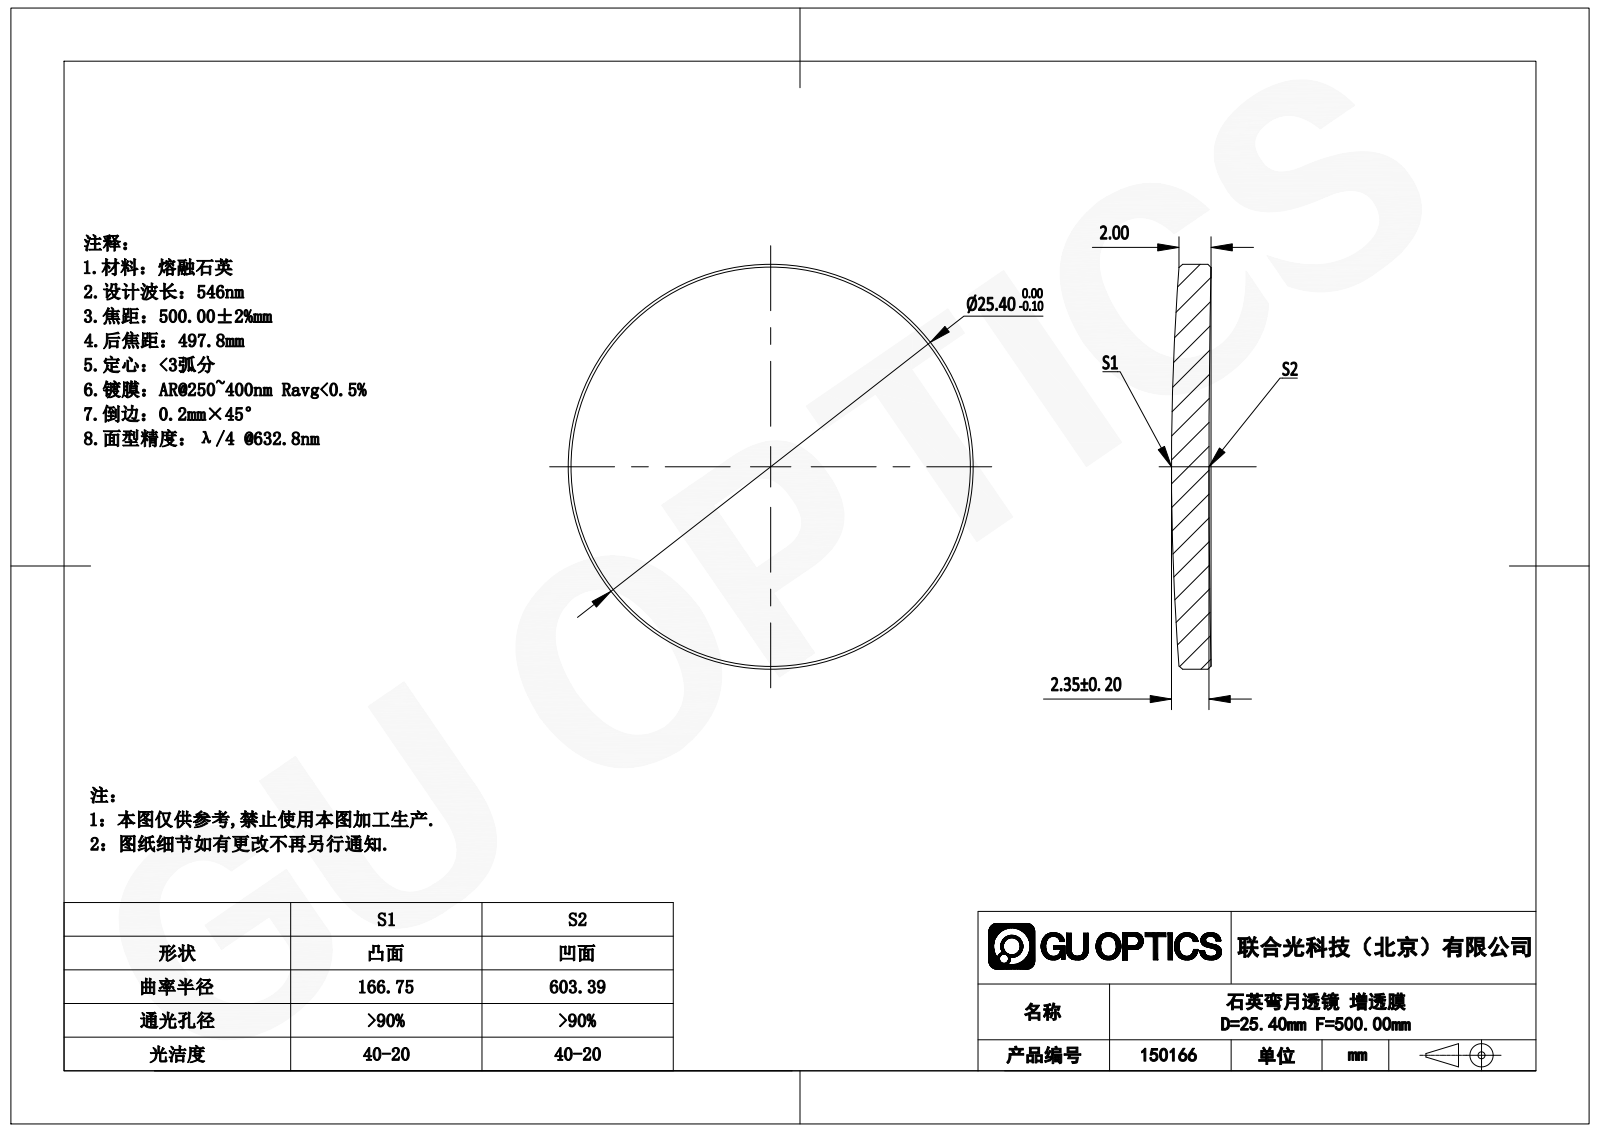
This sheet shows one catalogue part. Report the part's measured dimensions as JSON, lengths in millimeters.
{"part_name": "GLM2-025B-500-UV", "step_written_by": "SolidWorks 2022 (AUTOMOTIVE_DESIGN)", "units": "millimeters", "bodies": {"solids": 1, "faces": 10, "planar": 0, "cylindrical": 2, "other": 8}, "overall_size": [25.4, 25.4, 2.48], "volume_mm3": 1099, "surface_area_mm2": 1155, "round_bosses_or_shafts": [[25.4, 1]]}
